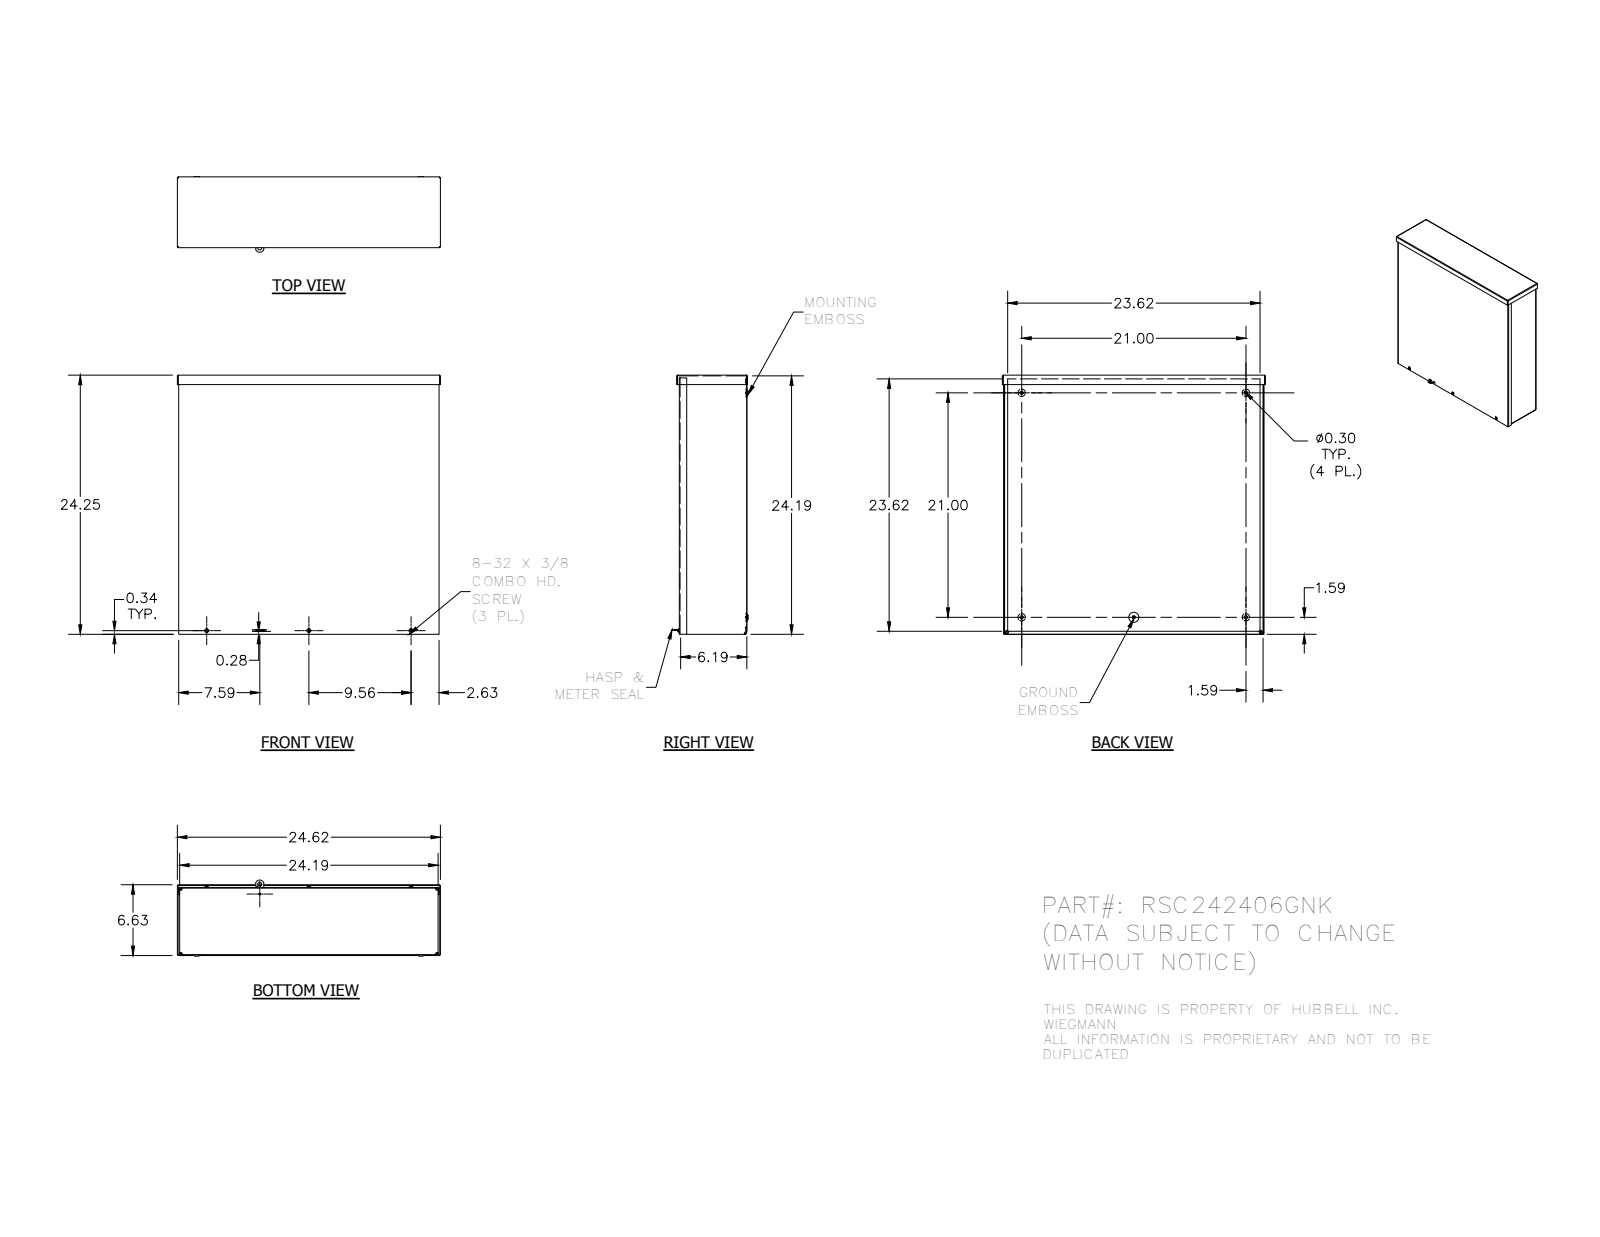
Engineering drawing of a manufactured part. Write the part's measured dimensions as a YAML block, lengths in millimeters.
part_name: "RSC242406GNK_WRAP; RSC2424GNK_LID; RSC2406GNK_CAP; 3183 (+3 more)"
step_written_by: "Autodesk Inventor 2014 (AUTOMOTIVE_DESIGN)"
units: millimeters
bodies: {solids: 8, faces: 407, planar: 173, cylindrical: 83, other: 151}
overall_size: [625.48, 615.96, 180.97]
volume: 2158000
surface_area: 2755000
round_holes:
  - {diameter: 7.95, count: 6}
  - {diameter: 7.62, count: 4}
  - {diameter: 3.76, count: 3}
  - {diameter: 3.17, count: 2}
  - {diameter: 3.96, count: 1}
  - {diameter: 4.19, count: 1}
  - {diameter: 9.52, count: 1}
round_bosses_or_shafts:
  - {diameter: 9.75, count: 3}
  - {diameter: 4.17, count: 3}
  - {diameter: 5.8, count: 1}
partial_cylinders:
  - {radius: 0.79, count: 8}
  - {radius: 2.37, count: 8}
  - {radius: 3.17, count: 8}
  - {radius: 4.75, count: 8}
  - {radius: 1.4, count: 4}
  - {radius: 1.57, count: 4}
  - {radius: 2.38, count: 4}
  - {radius: 2.97, count: 4}
face_to_face_distances: [1.58, 158.73, 157.15, 612.79, 1.59, 160.32, 158.74, 1.57, 614.37, 3.15]
hole_center_spacings: [533.4, 640.01, 592.13, 242.88, 242.89, 266.7, 268.06, 268.59]
